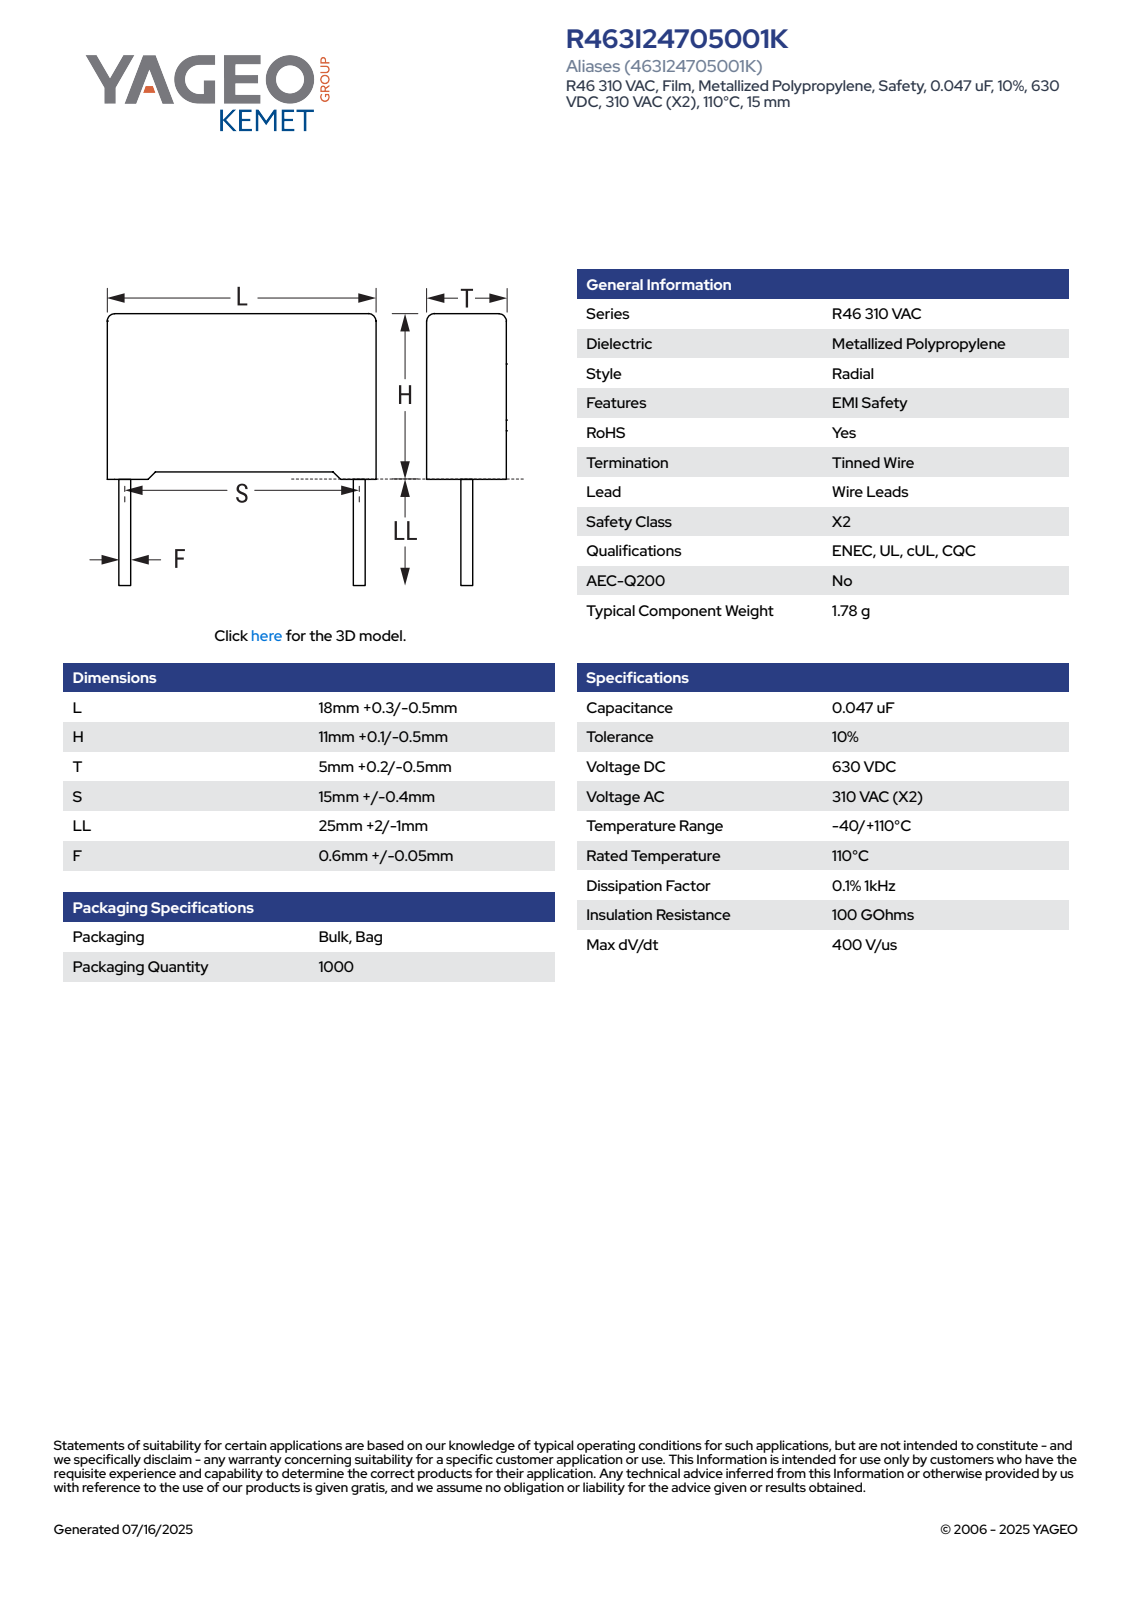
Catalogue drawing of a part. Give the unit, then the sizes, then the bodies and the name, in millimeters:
Units: millimetres
Overall size (bounding box): 38.1 × 18.3 × 5.21
Round bosses / shafts (diameter × count): ⌀0.65 ×2
Partial cylindrical surfaces — rounded edges, fillets, slot ends (radius × count): R0.5 ×4
Main face-to-face distances: 5.2, 10.35, 18.3, 0.61, 4.59, 0.37, 10.72, 0.38, 0.75, 11.1
Volume: 1 016 mm³ · Surface area: 855 mm²
Bodies: 4 solids, 85 faces (77 planar, 8 cylindrical, 0 other)
Part name (STEP PRODUCT): CFR_RB2_18X11X5_L18.3H11.1T5.2S15LL27F0.65
STEP written by: SolidWorks 2021 (AUTOMOTIVE_DESIGN)
